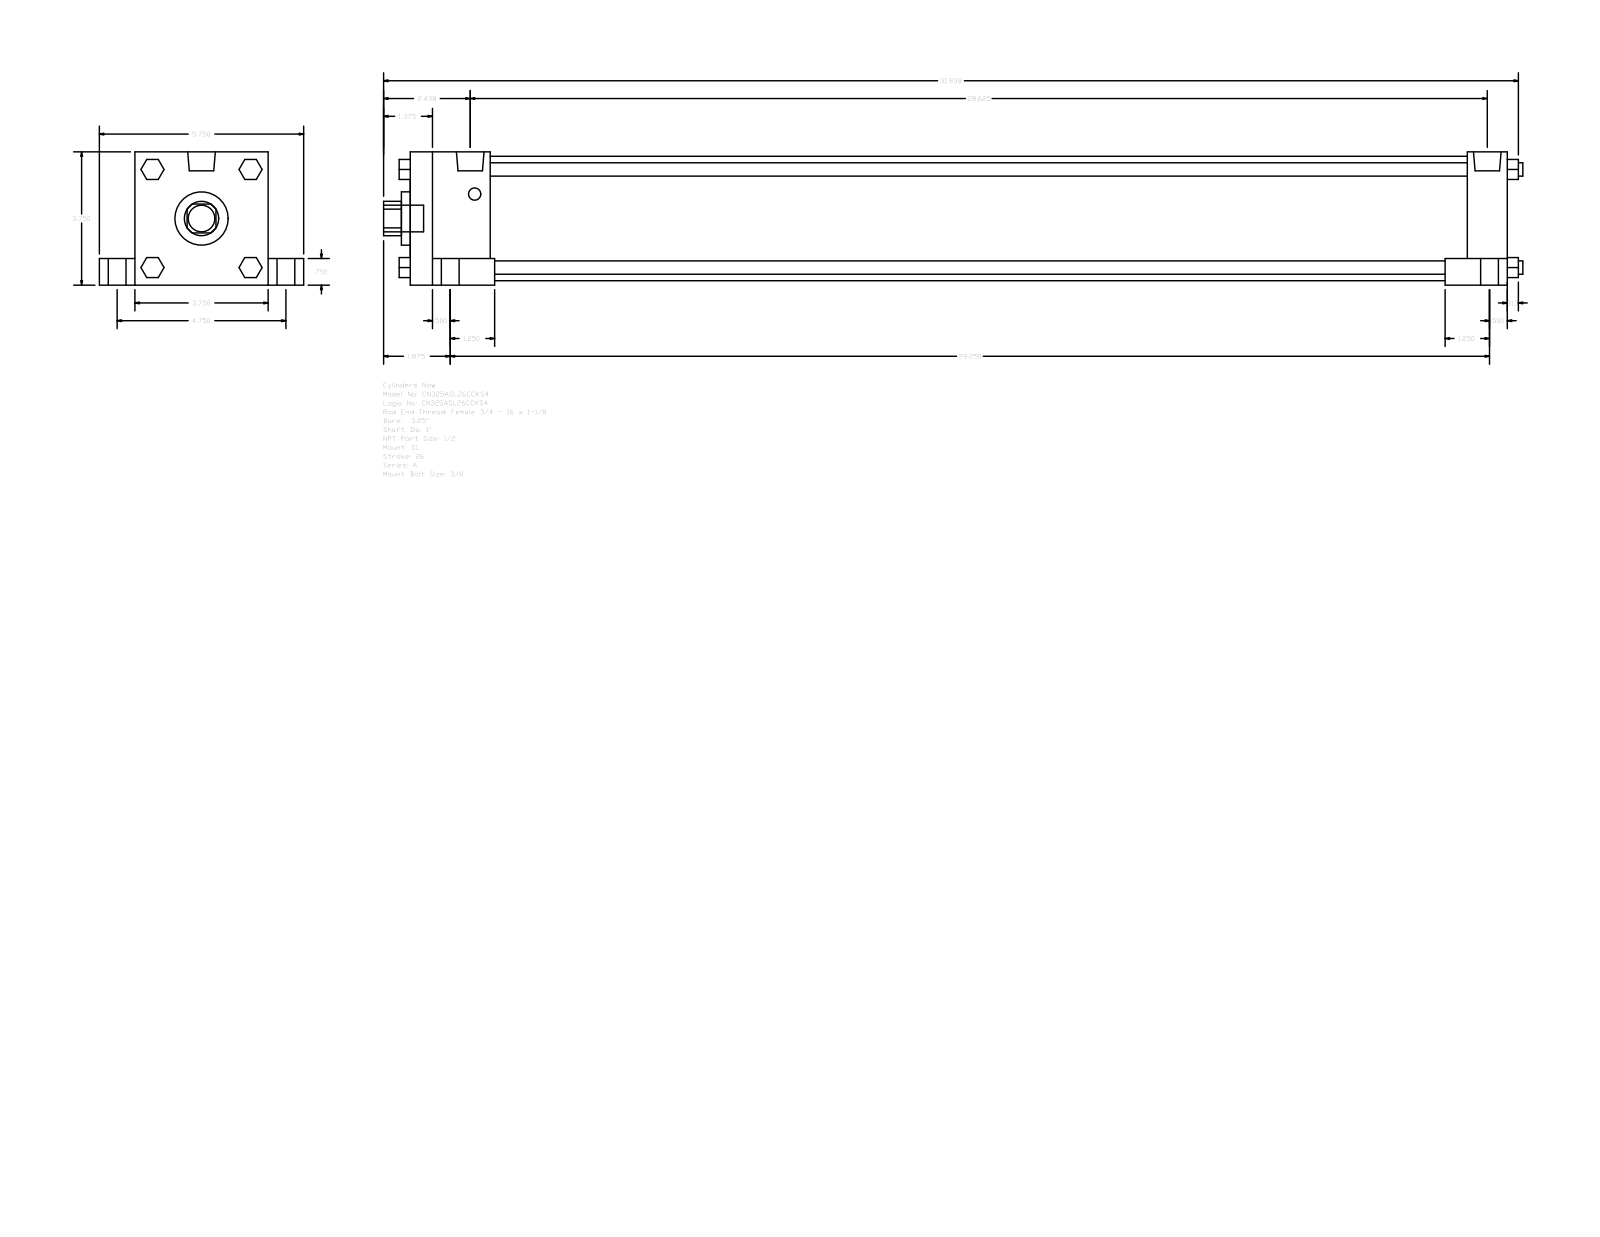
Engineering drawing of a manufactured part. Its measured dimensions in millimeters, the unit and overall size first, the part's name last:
Units: millimetres
Overall size (bounding box): 814.39 × 146.05 × 95.25
Round holes (diameter × count): ⌀25.4 ×1, ⌀38.1 ×1, ⌀88.9 ×1
Round bosses / shafts (diameter × count): ⌀19.05 ×5, ⌀12.7 ×4, ⌀9.53 ×4, ⌀8.73 ×4, ⌀19.77 ×2
Partial cylindrical surfaces — rounded edges, fillets, slot ends (radius × count): R12.29 ×1
Main face-to-face distances: 95.24, 784.22, 19.05, 25.41, 120.65, 76.19, 15.87, 28.57, 57.15, 755.65
Bodies: 0 solids, 150 faces (114 planar, 36 cylindrical, 0 other)
Part name (STEP PRODUCT): A_SL__0325_1
STEP written by: GSSL Pune (CONFIG_CONTROL_DESIGN)
